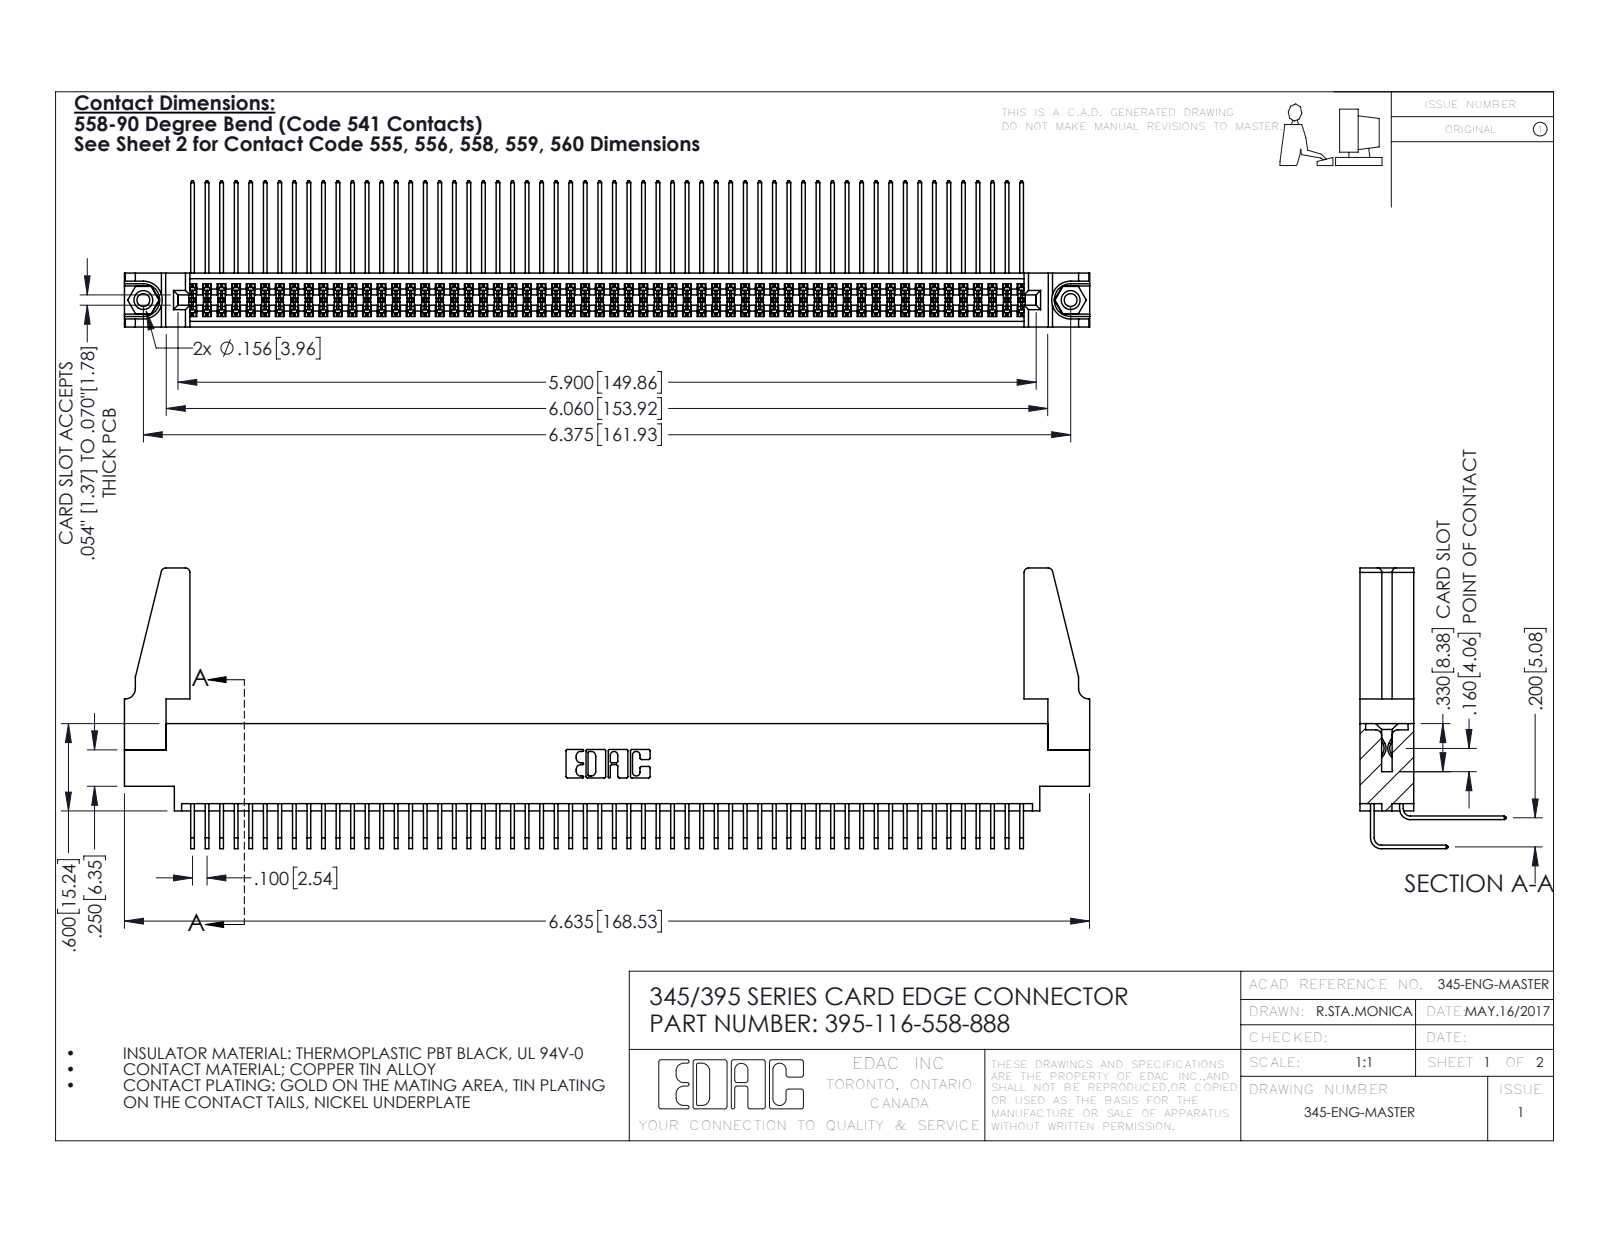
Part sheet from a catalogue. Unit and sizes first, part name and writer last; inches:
Units: inches
Overall size (bounding box): 6.636 × 1.929 × 1.005
Round holes (diameter × count): ⌀0.089 ×2, ⌀0.125 ×2, ⌀0.156 ×2, ⌀0.064 ×1
Round bosses / shafts (diameter × count): ⌀0.155 ×2
Partial cylindrical surfaces — rounded edges, fillets, slot ends (radius × count): R0.006 ×174, R0.01 ×22, R0.03 ×8, R0.007 ×6, R0.031 ×6, R0.026 ×3, R0.014 ×2, R0.019 ×2
Main face-to-face distances: 0.072, 0.298, 0.2, 0.37, 0.098, 0.272, 0.025, 0.225, 0.175, 0.025
Hole centre spacings: 0.27, 6.139, 6.375
Volume: 1.241 in³ · Surface area: 49.55 in²
Bodies: 121 solids, 6286 faces (4216 planar, 2054 cylindrical, 16 other)
Part name (STEP PRODUCT): 345-220-078_345-220-088; 345-250-001_345-250-001-102; 345-292-001_558 559 Tail - 1; 395-116-558-888 (+2 more)
STEP written by: SolidWorks 2016 (CONFIG_CONTROL_DESIGN)
